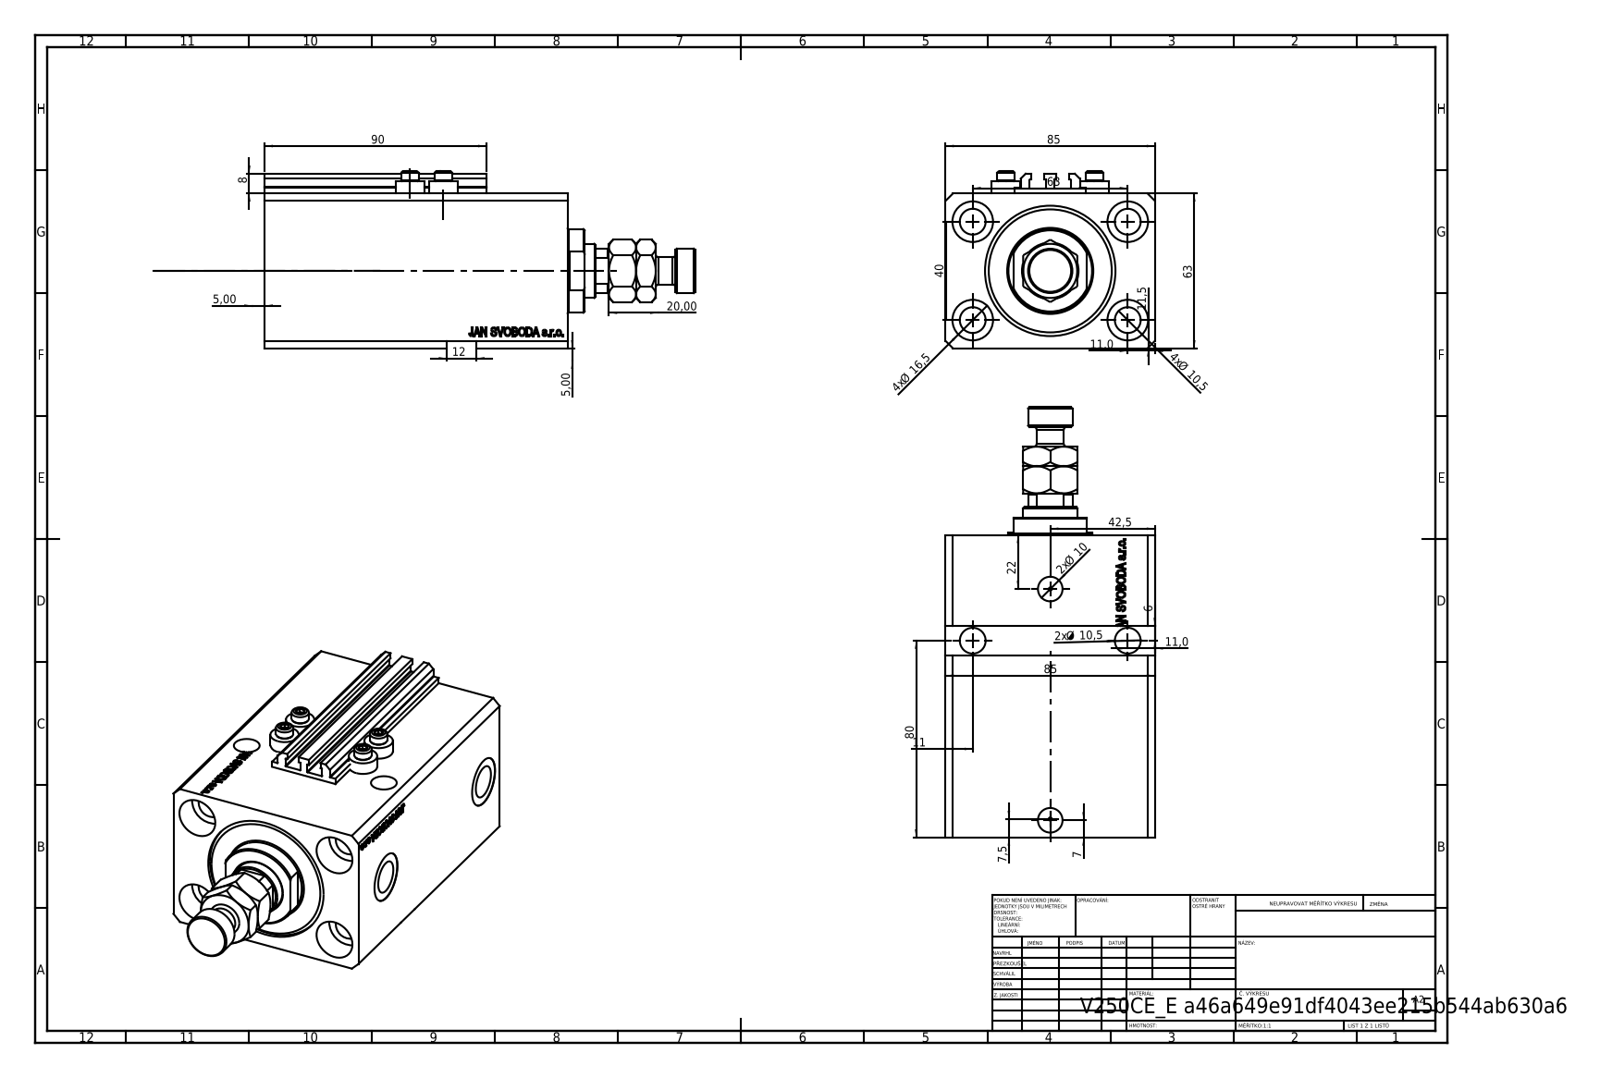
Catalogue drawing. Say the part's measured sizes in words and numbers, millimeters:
The part is named "V250CE_E_Body; V250CE_VC_E; MFA; ALLEN BOLT V250CE (+1 more)". Its 3-D file was written by "SolidWorks 2019 (CONFIG_CONTROL_DESIGN)". It is 9 solids with 1139 faces: 551 planar, 130 cylindrical and 458 other. Overall it measures 174.9 by 85 by 72 millimeters. Its volume is 575 129 cubic millimeters and its surface area 122 675 square millimeters. Round holes: 6 of diameter 10.5, 4 of diameter 1.25, 4 of diameter 4, 4 of diameter 16.5, 2 of diameter 10, 2 of diameter 13.16, 2 of diameter 20, 1 of diameter 12.5, 1 of diameter 22, 1 of diameter 40, 1 of diameter 53. Round bosses or shafts: 4 of diameter 11.6, 4 of diameter 7, 1 of diameter 34, 1 of diameter 18, 1 of diameter 11. Partial cylindrical surfaces (rounded edges, fillets, slot ends): 10 of radius 0.2, 1 of radius 10.5. The main face-to-face distances are 63, 85, 123, 95.9, 27.1, 11.4, 84.5, 111.6, 3, 65. The hole center spacings are 37.31, 63, 13.6, 15.4, 24.96, 33.62, 36, 37.86.
